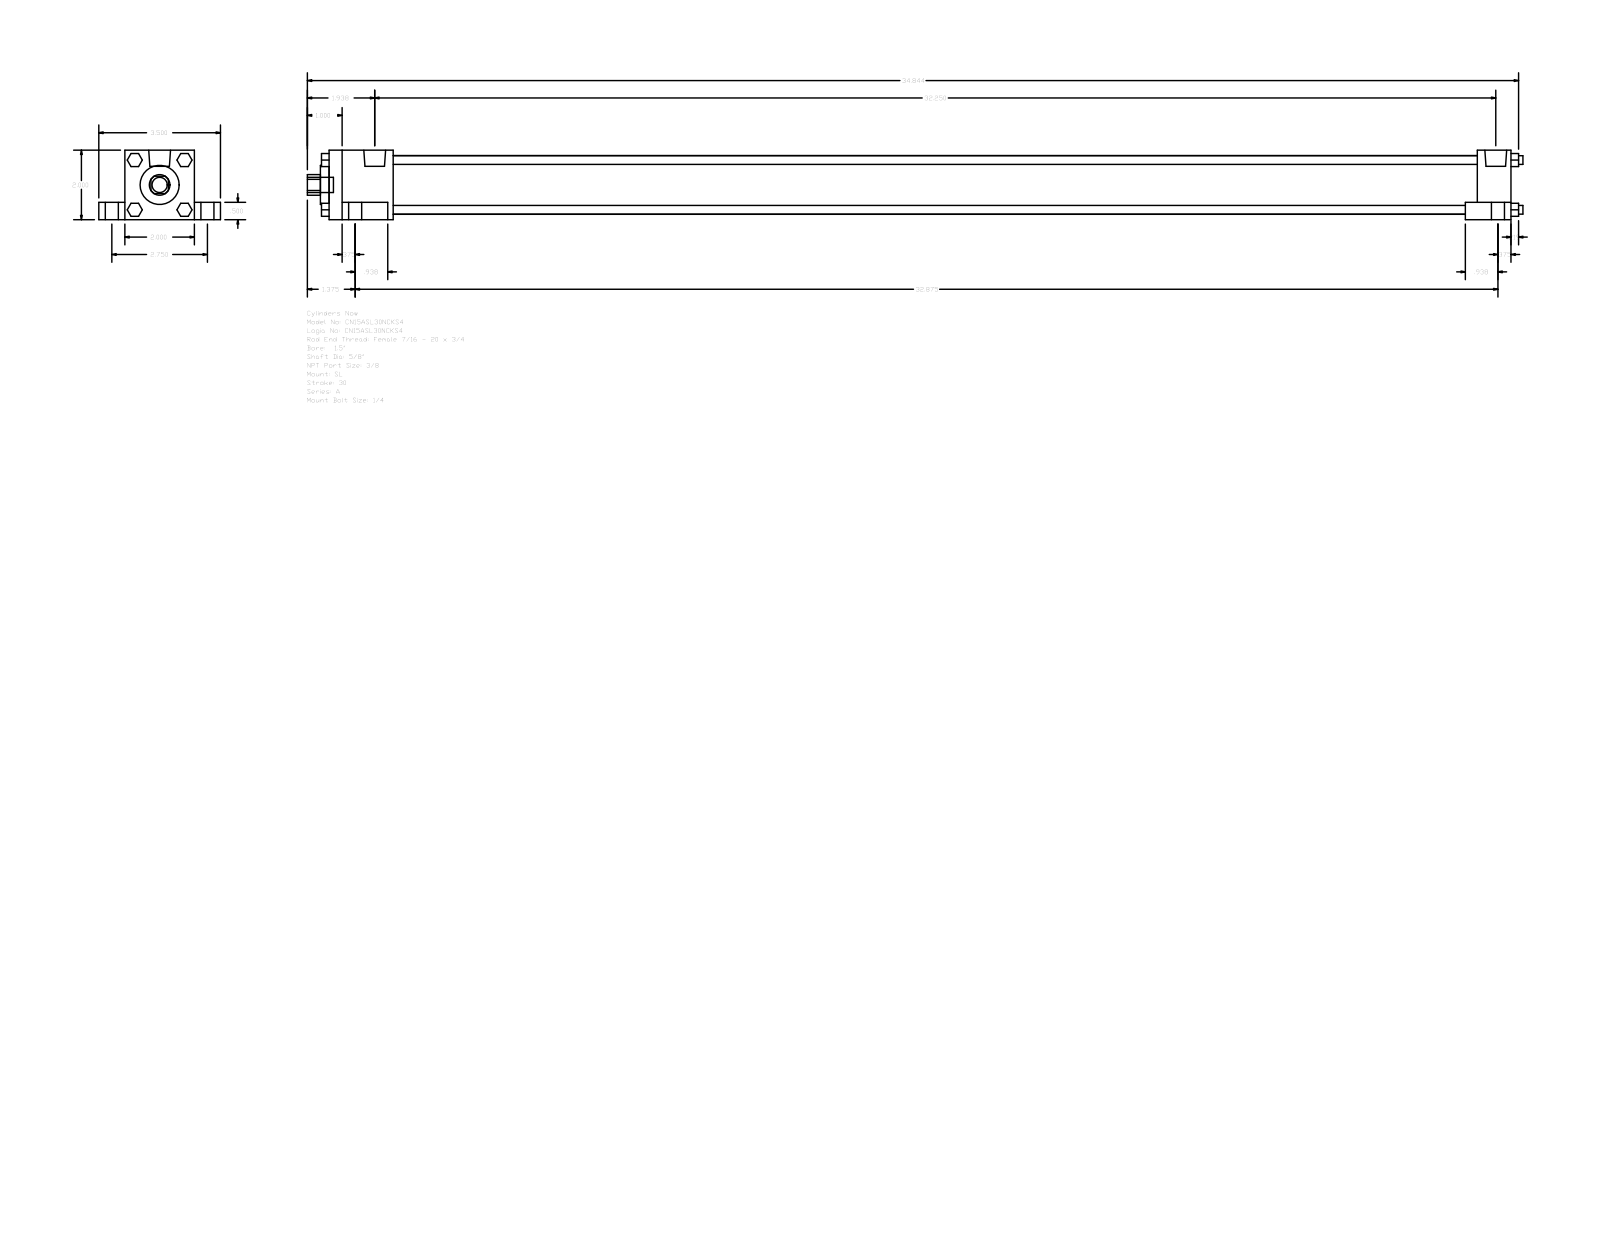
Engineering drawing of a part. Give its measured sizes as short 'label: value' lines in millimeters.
name: A_SL__0150_0.625
written by: GSSL Pune (CONFIG_CONTROL_DESIGN)
unit: mm
bodies: 0 solids, 148 faces (112 planar, 36 cylindrical, 0 other)
size: 888.21 × 88.9 × 50.8
holes: 1× ⌀15.88, 1× ⌀28.57, 1× ⌀42.93
bosses: 4× ⌀15.88, 4× ⌀9.53, 4× ⌀6.35, 4× ⌀5.56, 2× ⌀15.93, 1× ⌀11.11
rounds: 1× R7.54
face distances: 50.8, 19.05, 12.7, 38.1, 69.85, 863.6, 9.52, 33.34, 838.99, 24.61
